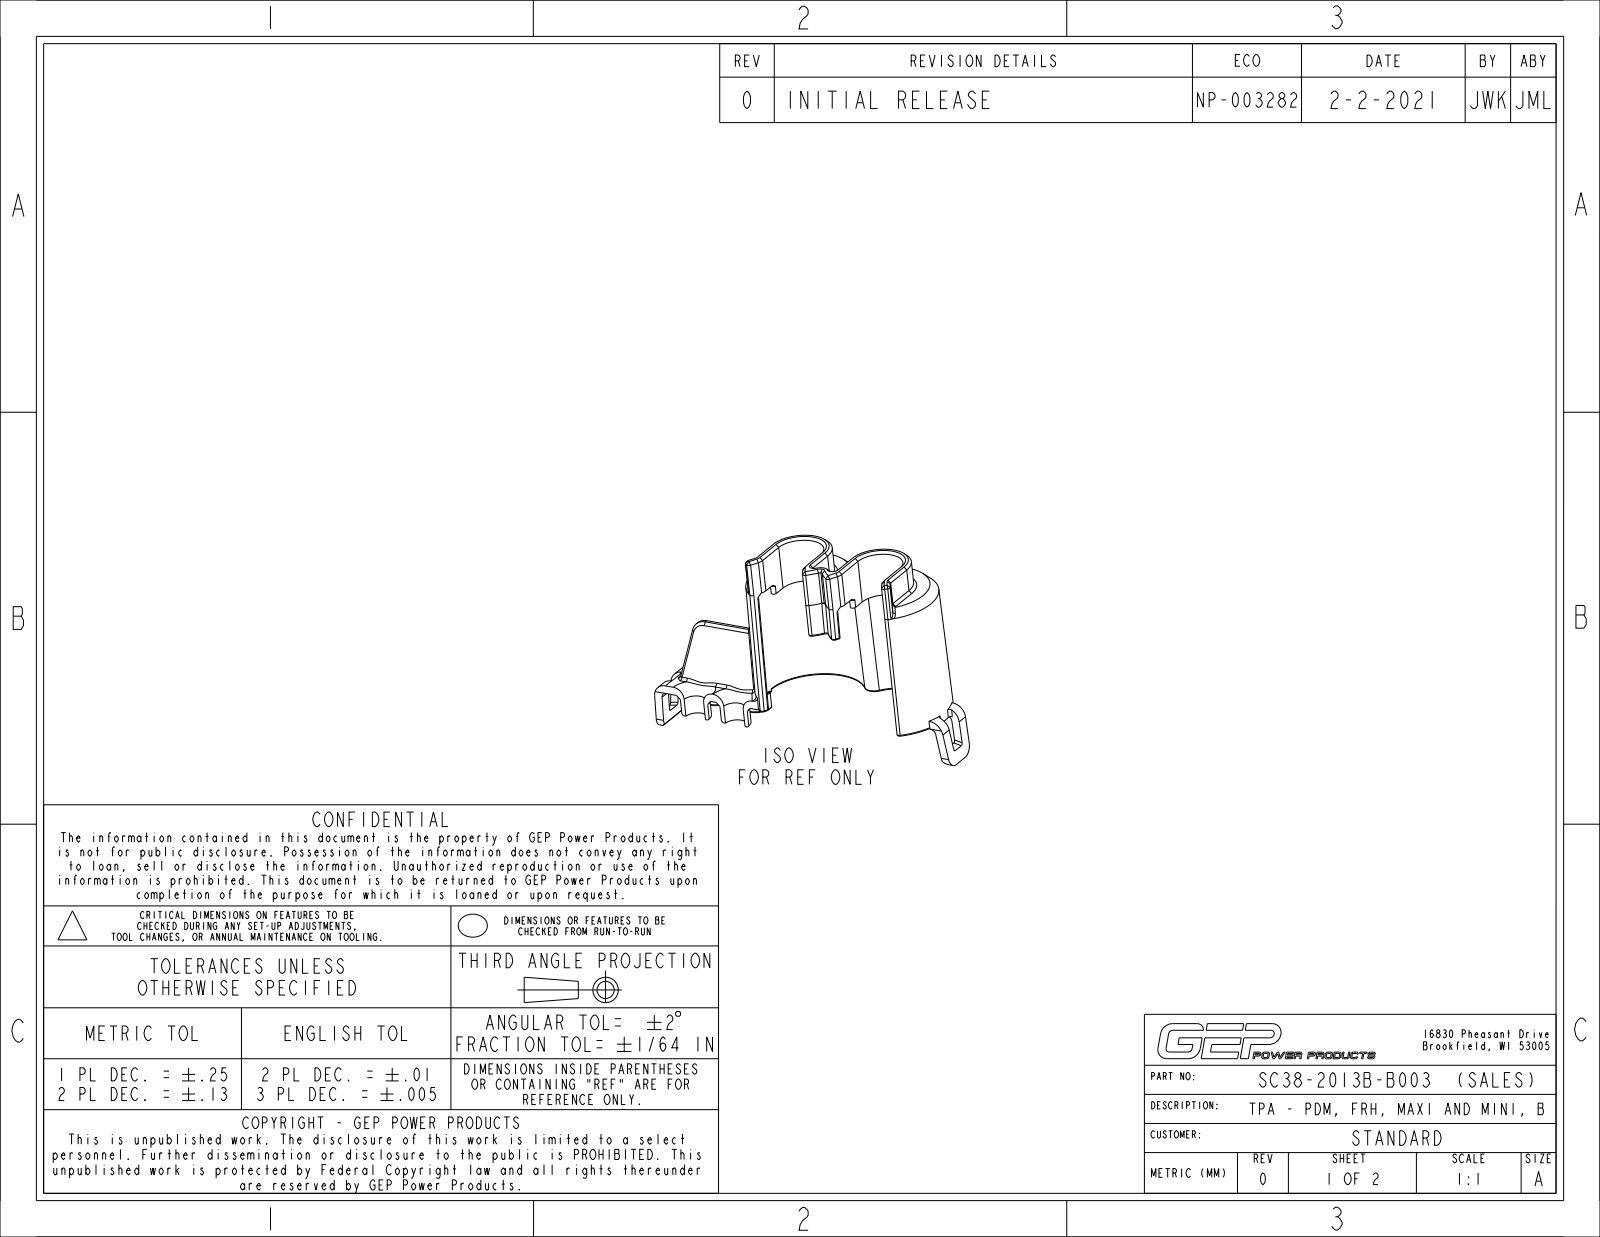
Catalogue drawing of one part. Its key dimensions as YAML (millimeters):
part_name: "PC38-2013B-B003_NCF; SC38-2013B-B003_NCF_ASM"
step_written_by: "CREO PARAMETRIC BY PTC INC, 2017110 (CONFIG_CONTROL_DESIGN)"
units: millimeters
bodies: {solids: 1, faces: 323, planar: 123, cylindrical: 71, other: 129}
overall_size: [57.9, 36.5, 18.8]
volume: 3993
surface_area: 5839
round_holes:
  - {diameter: 3, count: 2}
partial_cylinders:
  - {radius: 0.5, count: 21}
  - {radius: 2, count: 13}
  - {radius: 0.25, count: 4}
  - {radius: 0.4, count: 4}
  - {radius: 2.8, count: 4}
  - {radius: 1, count: 2}
  - {radius: 2.5, count: 2}
  - {radius: 5.75, count: 2}
face_to_face_distances: [1.5, 1.4, 22.6, 24, 2, 20.6, 3.4, 3.15, 4.65, 10]
hole_center_spacings: [4]
